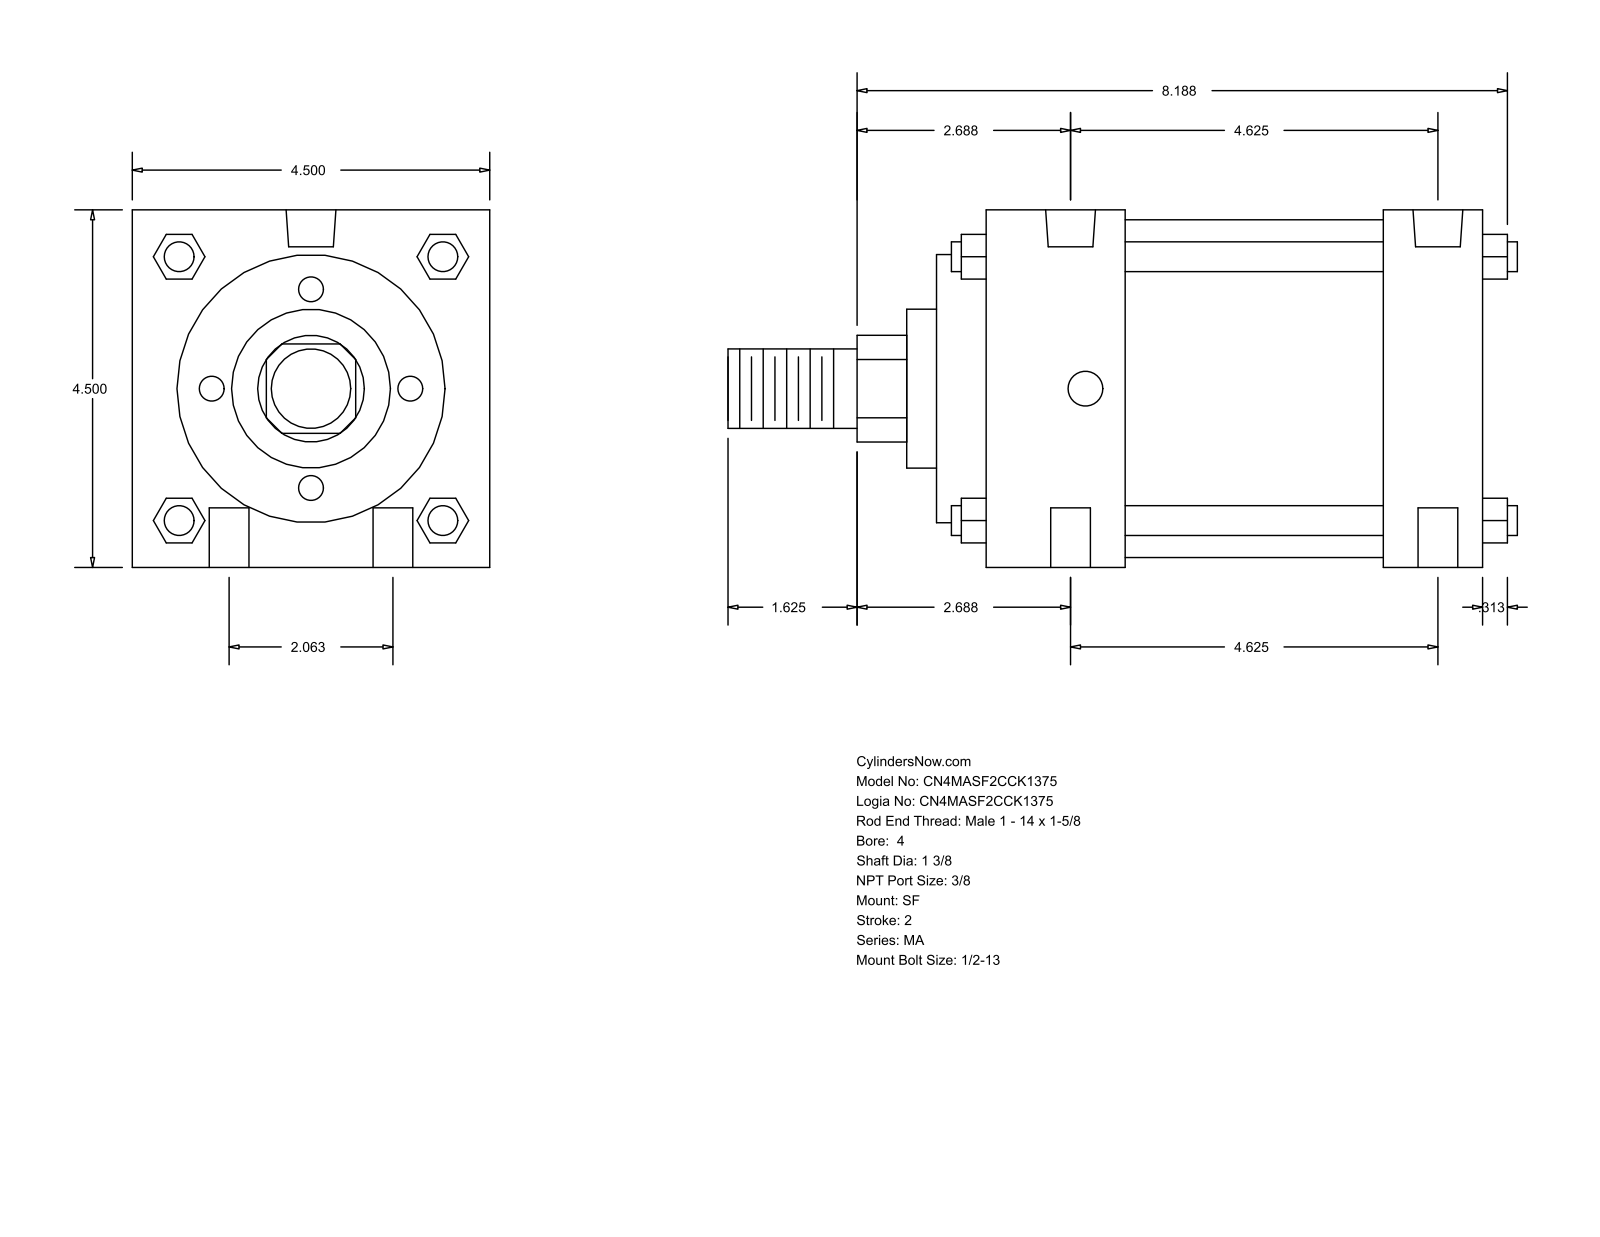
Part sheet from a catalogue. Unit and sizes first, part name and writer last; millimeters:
Units: millimetres
Overall size (bounding box): 252.41 × 114.3 × 114.3
Round holes (diameter × count): ⌀12.7 ×4, ⌀11.11 ×2, ⌀15.93 ×2
Round bosses / shafts (diameter × count): ⌀9.53 ×4, ⌀107.95 ×1, ⌀85.72 ×1, ⌀50.8 ×1, ⌀34.92 ×1, ⌀25.4 ×1
Partial cylindrical surfaces — rounded edges, fillets, slot ends (radius × count): R17.06 ×1
Main face-to-face distances: 114.3, 158.76, 15.87, 174.63, 142.88, 127.01, 31.75, 60.32, 44.45, 82.56
Hole centre spacings: 26.19, 120.36, 117.48, 52.38, 128.63, 107.94
Bodies: 0 solids, 126 faces (95 planar, 31 cylindrical, 0 other)
Part name (STEP PRODUCT): MA_SF__0400_1.375
STEP written by: GSSL Pune (CONFIG_CONTROL_DESIGN)
